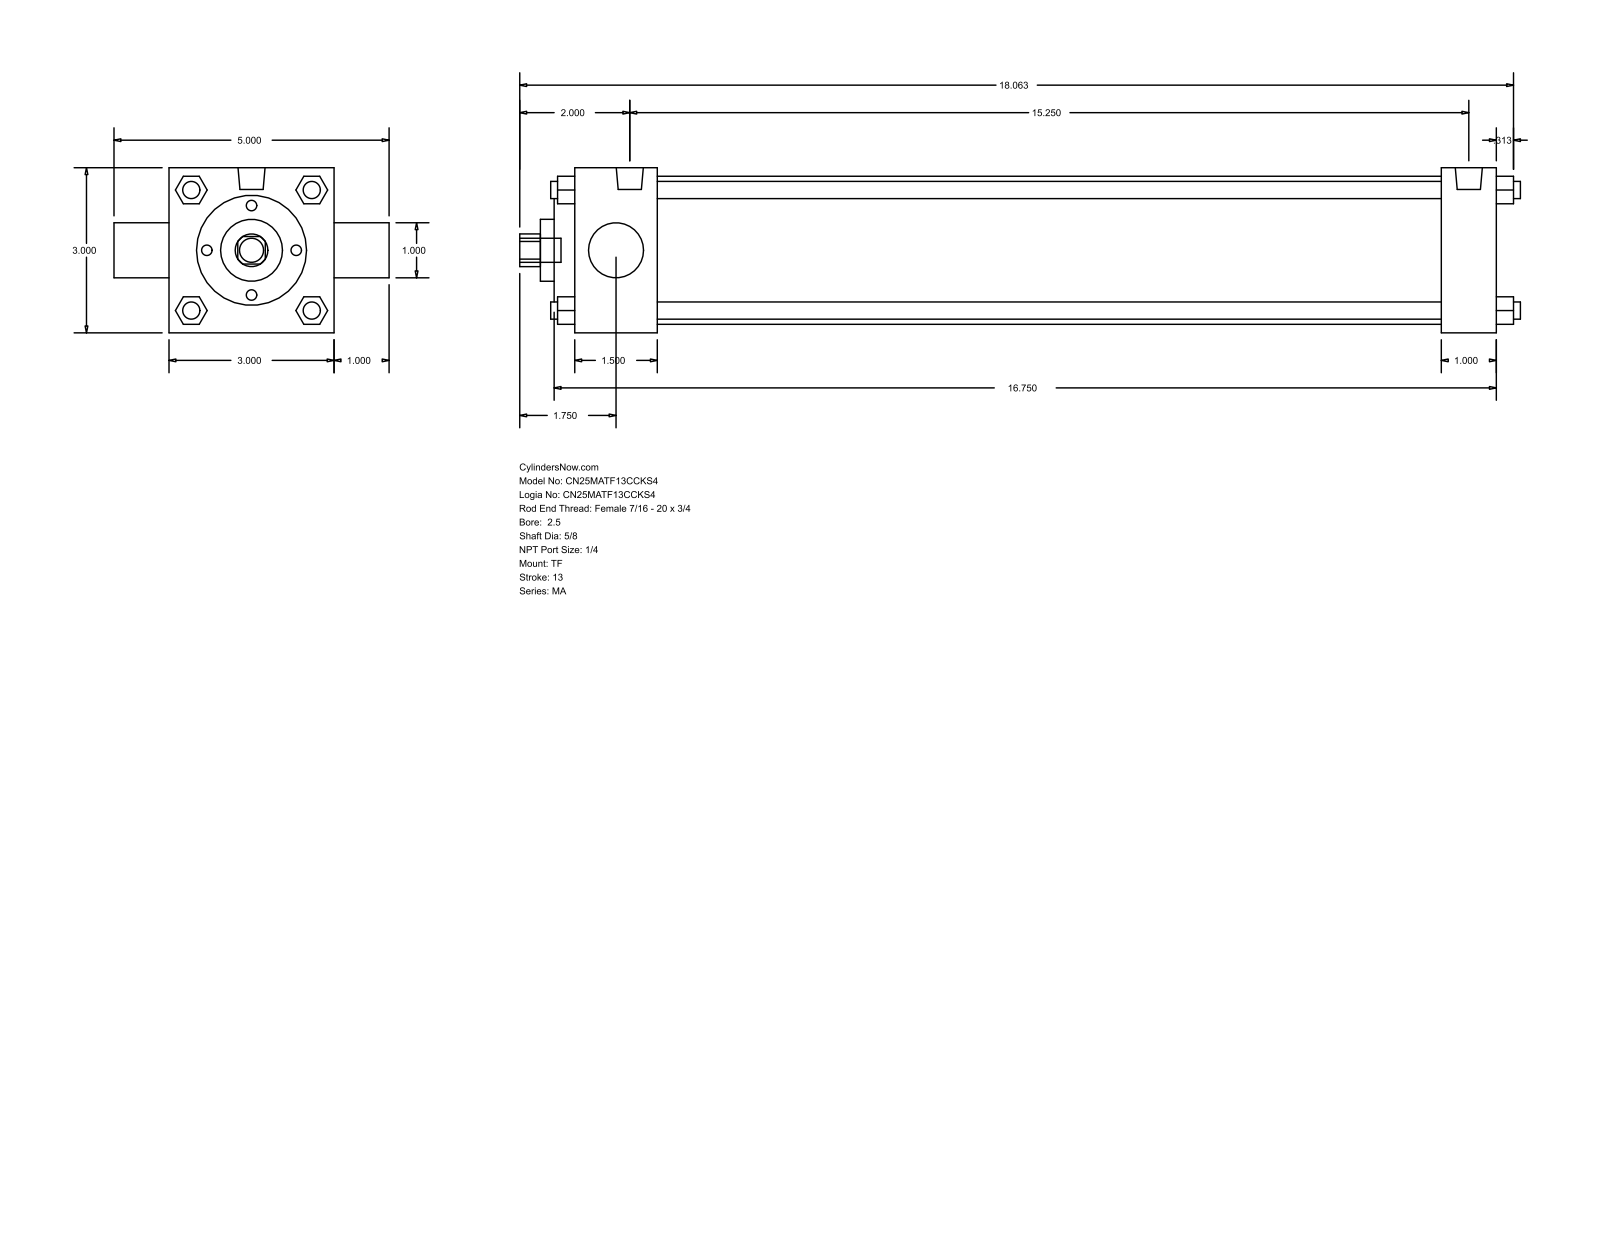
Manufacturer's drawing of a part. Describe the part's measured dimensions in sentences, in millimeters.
The part is named "MA_TF__0250_0.625". Its 3-D file was written by "GSSL Pune (CONFIG_CONTROL_DESIGN)". It is 0 solids with 122 faces: 93 planar, 29 cylindrical and 0 other. Overall it measures 461.96 by 127 by 76.2 millimeters. Round holes: 1 of diameter 15.88, 1 of diameter 25.4, 1 of diameter 28.57, 1 of diameter 50.8, 1 of diameter 68.33. Round bosses or shafts: 7 of diameter 7.94, 2 of diameter 12.49, 1 of diameter 11.11. Partial cylindrical surfaces (rounded edges, fillets, slot ends): 1 of radius 7.54. The main face-to-face distances are 76.2, 425.45, 25.4, 38.1, 400.05, 361.95, 387.35, 12.7, 9.52, 47.62.
